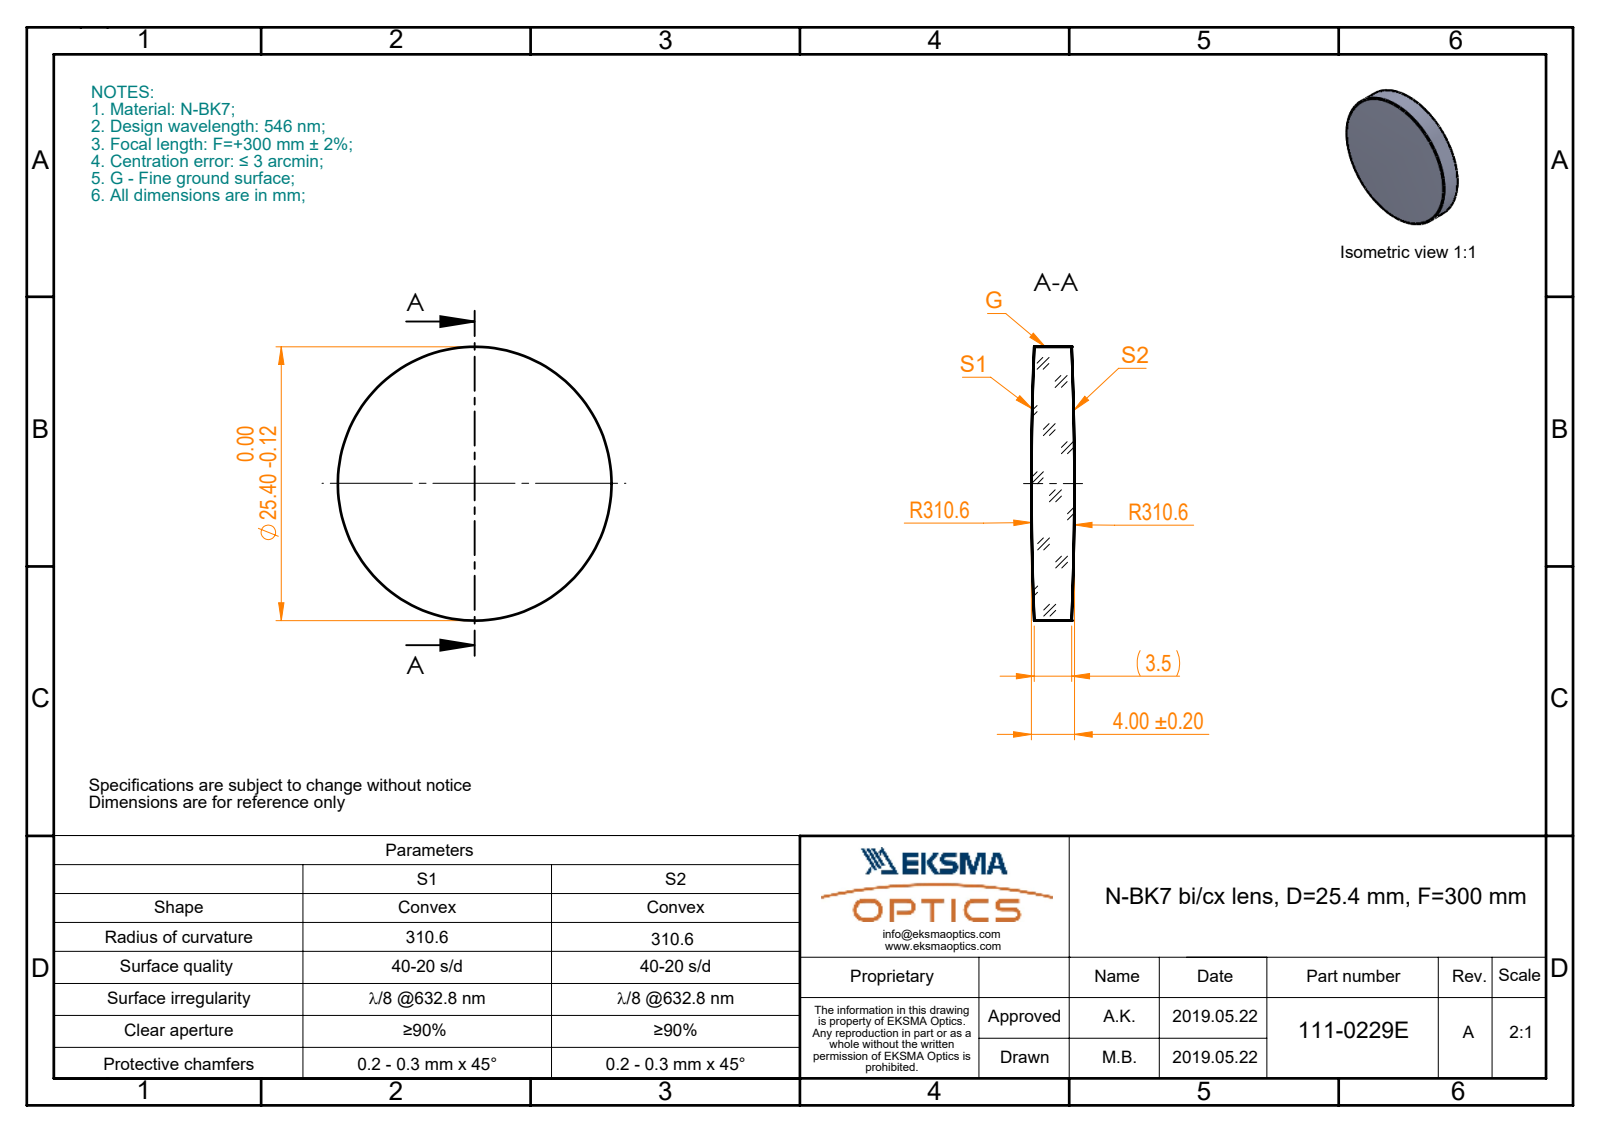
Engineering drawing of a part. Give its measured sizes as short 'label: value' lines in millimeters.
name: 111-0229E BK7 bi-cx 25.4 F300
written by: SolidWorks 2017 (CONFIG_CONTROL_DESIGN)
unit: mm
bodies: 1 solid, 6 faces (0 planar, 2 cylindrical, 4 other)
size: 25.4 × 25.4 × 4
volume: 1 895 mm³; area: 1 292 mm²
bosses: 1× ⌀25.4
